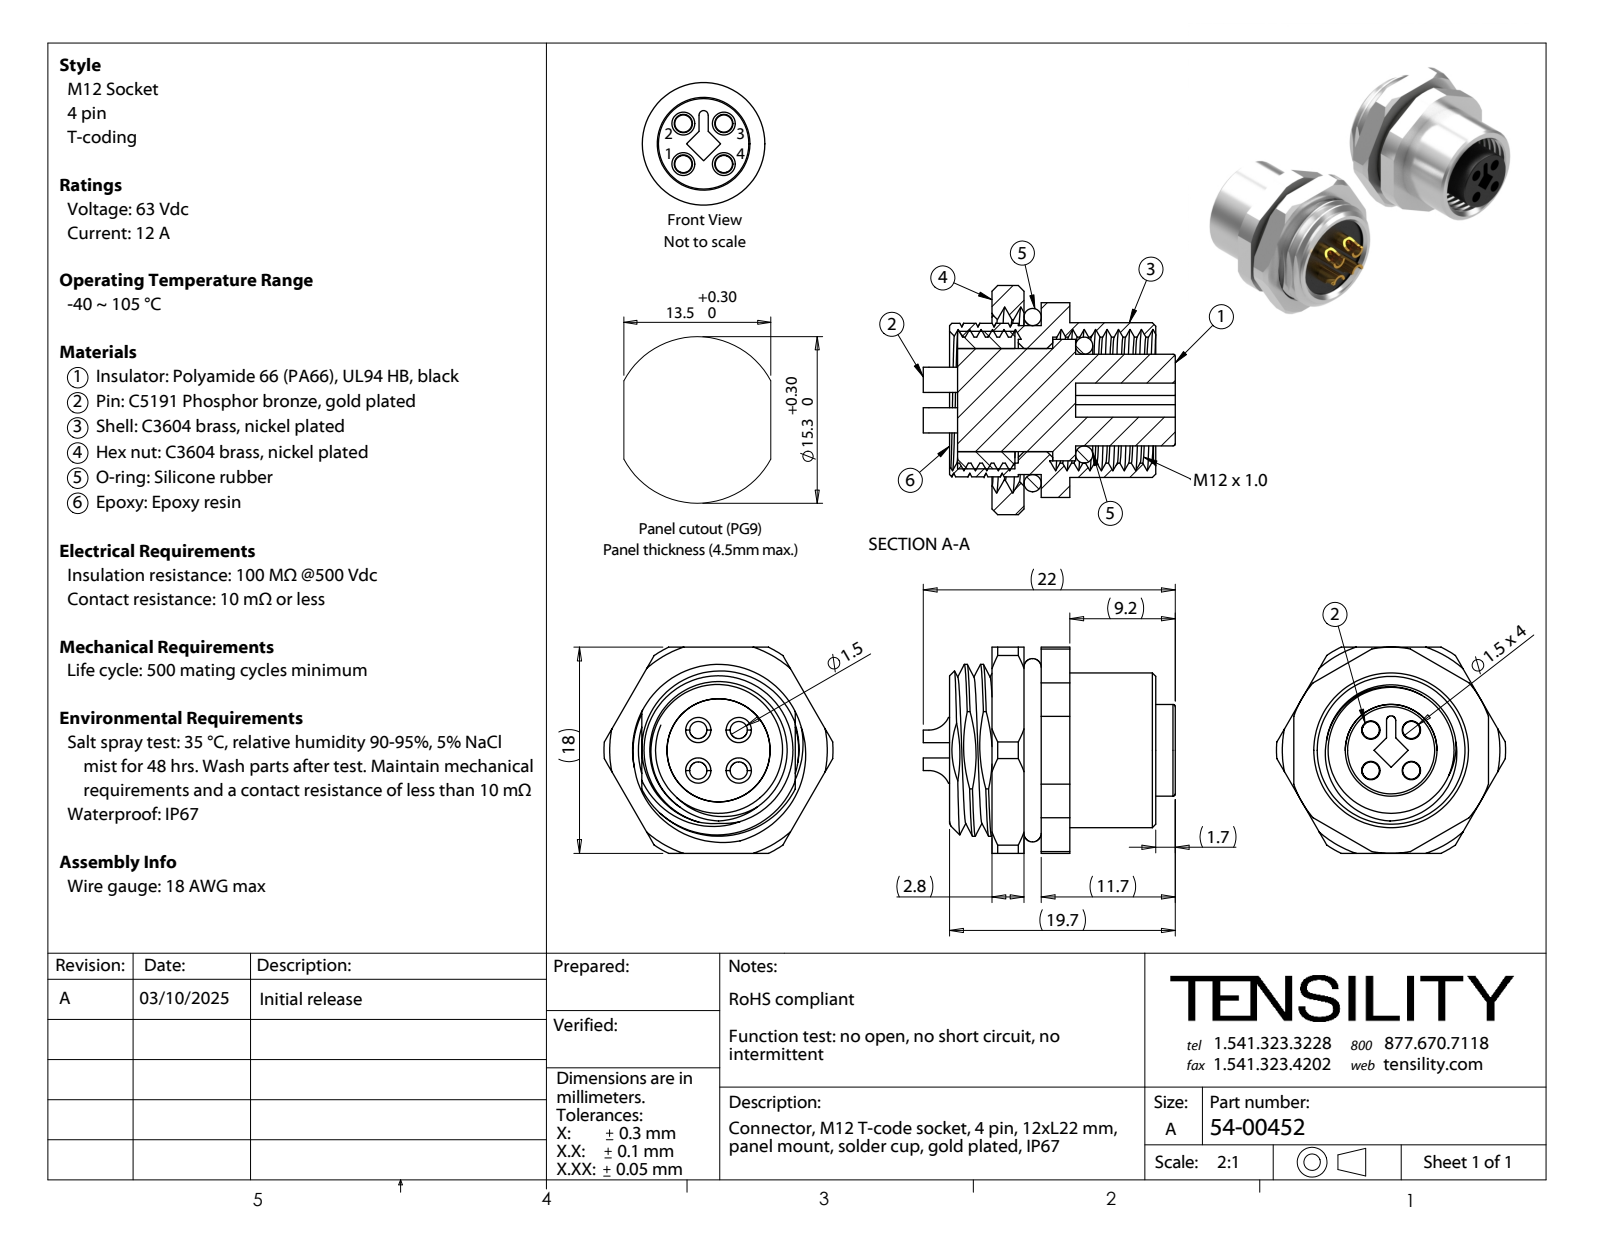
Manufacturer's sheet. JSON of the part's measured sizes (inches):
{"part_name": "54-00452-02; 54-00452-04; 54-00452-03; 54-00452 (+3 more)", "step_written_by": "SolidWorks 2021 (CONFIG_CONTROL_DESIGN)", "units": "inches", "bodies": {"solids": 10, "faces": 322, "planar": 102, "cylindrical": 136, "other": 84}, "overall_size": [0.866, 0.787, 0.709], "volume_in3": 0.169, "surface_area_in2": 9.033, "round_holes": [[0.059, 4], [0.063, 4], [0.354, 1], [0.433, 1], [0.551, 1]], "round_bosses_or_shafts": [[0.087, 4], [0.531, 1], [0.512, 1], [0.472, 1], [0.417, 1], [0.315, 1]], "partial_cylinders_radius": [[0.073, 2], [0.016, 1], [0.295, 1], [0.354, 1], [0.394, 1]], "face_to_face_distances": [0.118, 0.098, 0.287, 0.079, 0.059, 0.209, 0.386, 0.02, 0.091, 0.157], "hole_center_spacings": [0.098, 0.139, 0.197]}
